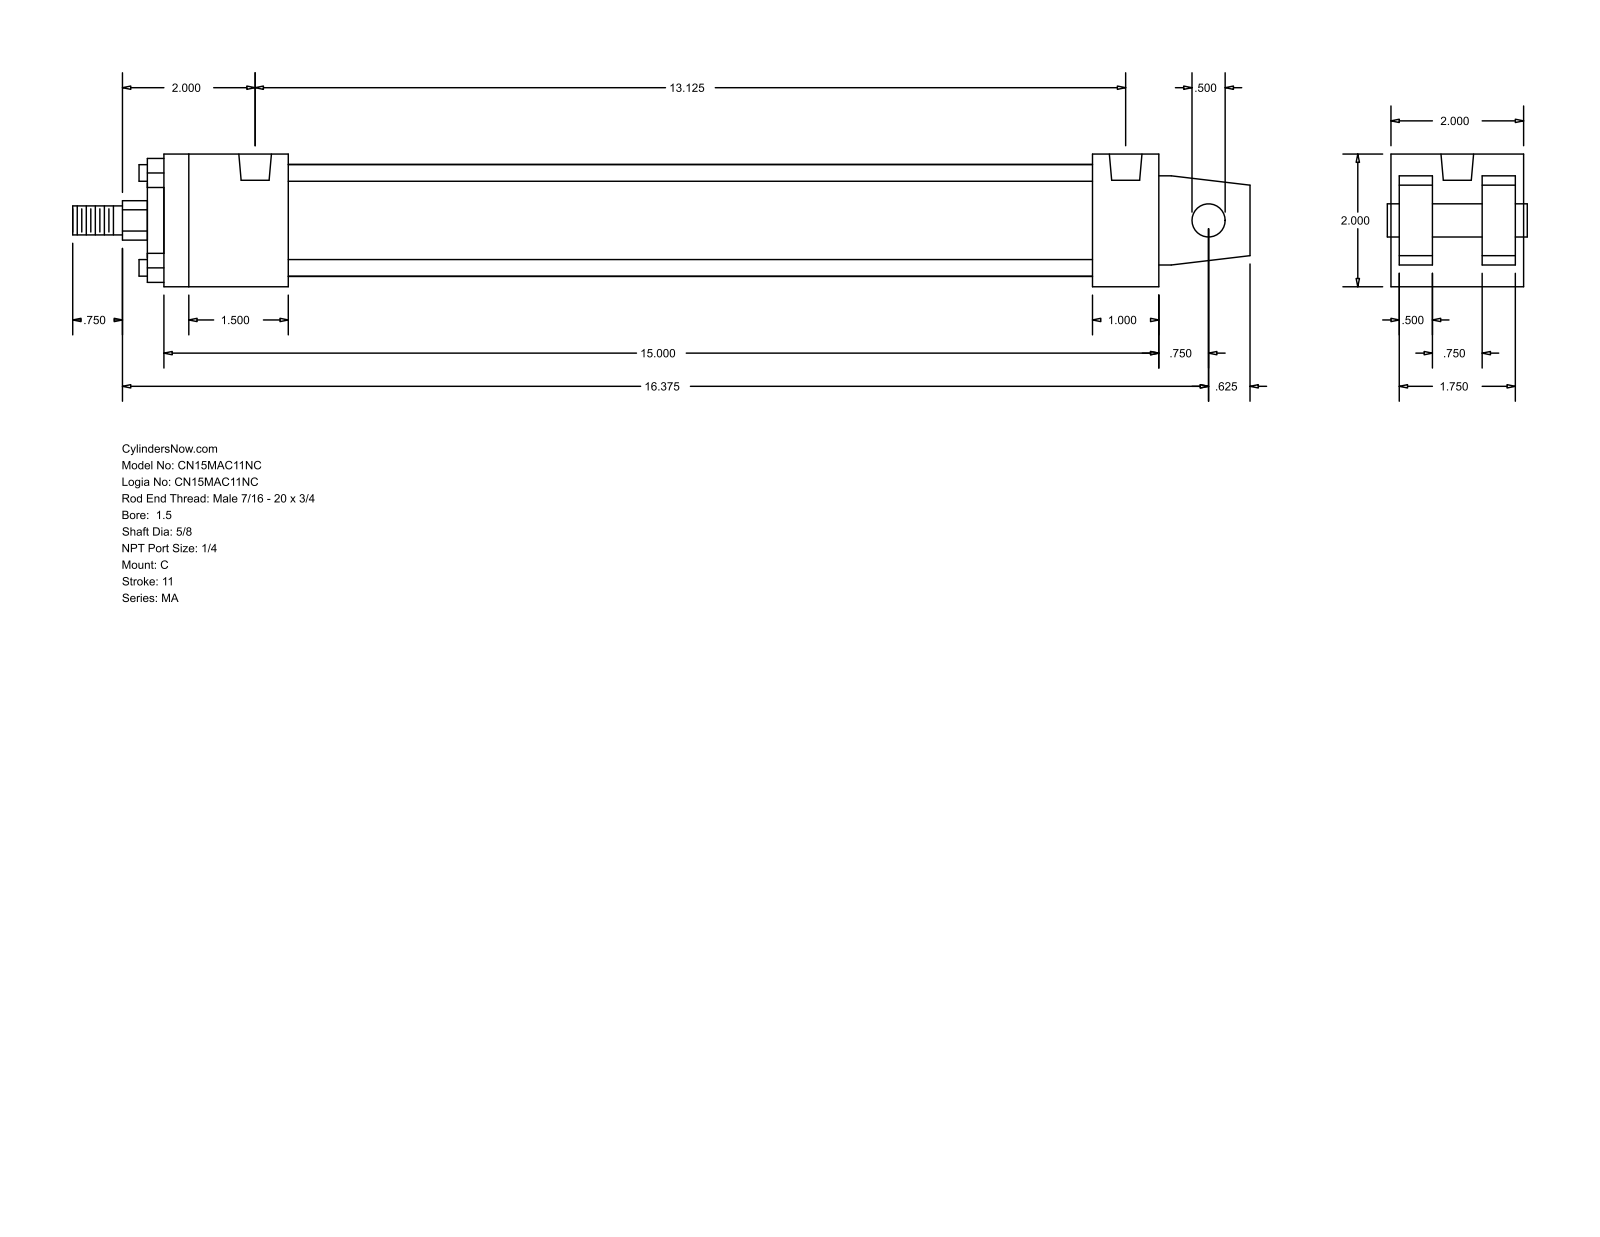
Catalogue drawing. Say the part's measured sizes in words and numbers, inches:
The part is named "MA_C__0150_0.625". Its 3-D file was written by "GSSL Pune (CONFIG_CONTROL_DESIGN)". It is 0 solids with 103 faces: 76 planar, 27 cylindrical and 0 other. Overall it measures 17.75 by 2 by 2 inches. Round holes: 4 of diameter 0.313, 2 of diameter 0.492. Round bosses or shafts: 4 of diameter 0.25, 1 of diameter 1.69, 1 of diameter 1.125, 1 of diameter 0.625, 1 of diameter 0.5, 1 of diameter 0.437. Partial cylindrical surfaces (rounded edges, fillets, slot ends): 1 of radius 0.297. The main face-to-face distances are 2, 0.5, 1.375, 0.625, 0.125, 1.875, 1.25, 15, 1, 14. The hole center spacings are 13.125.
